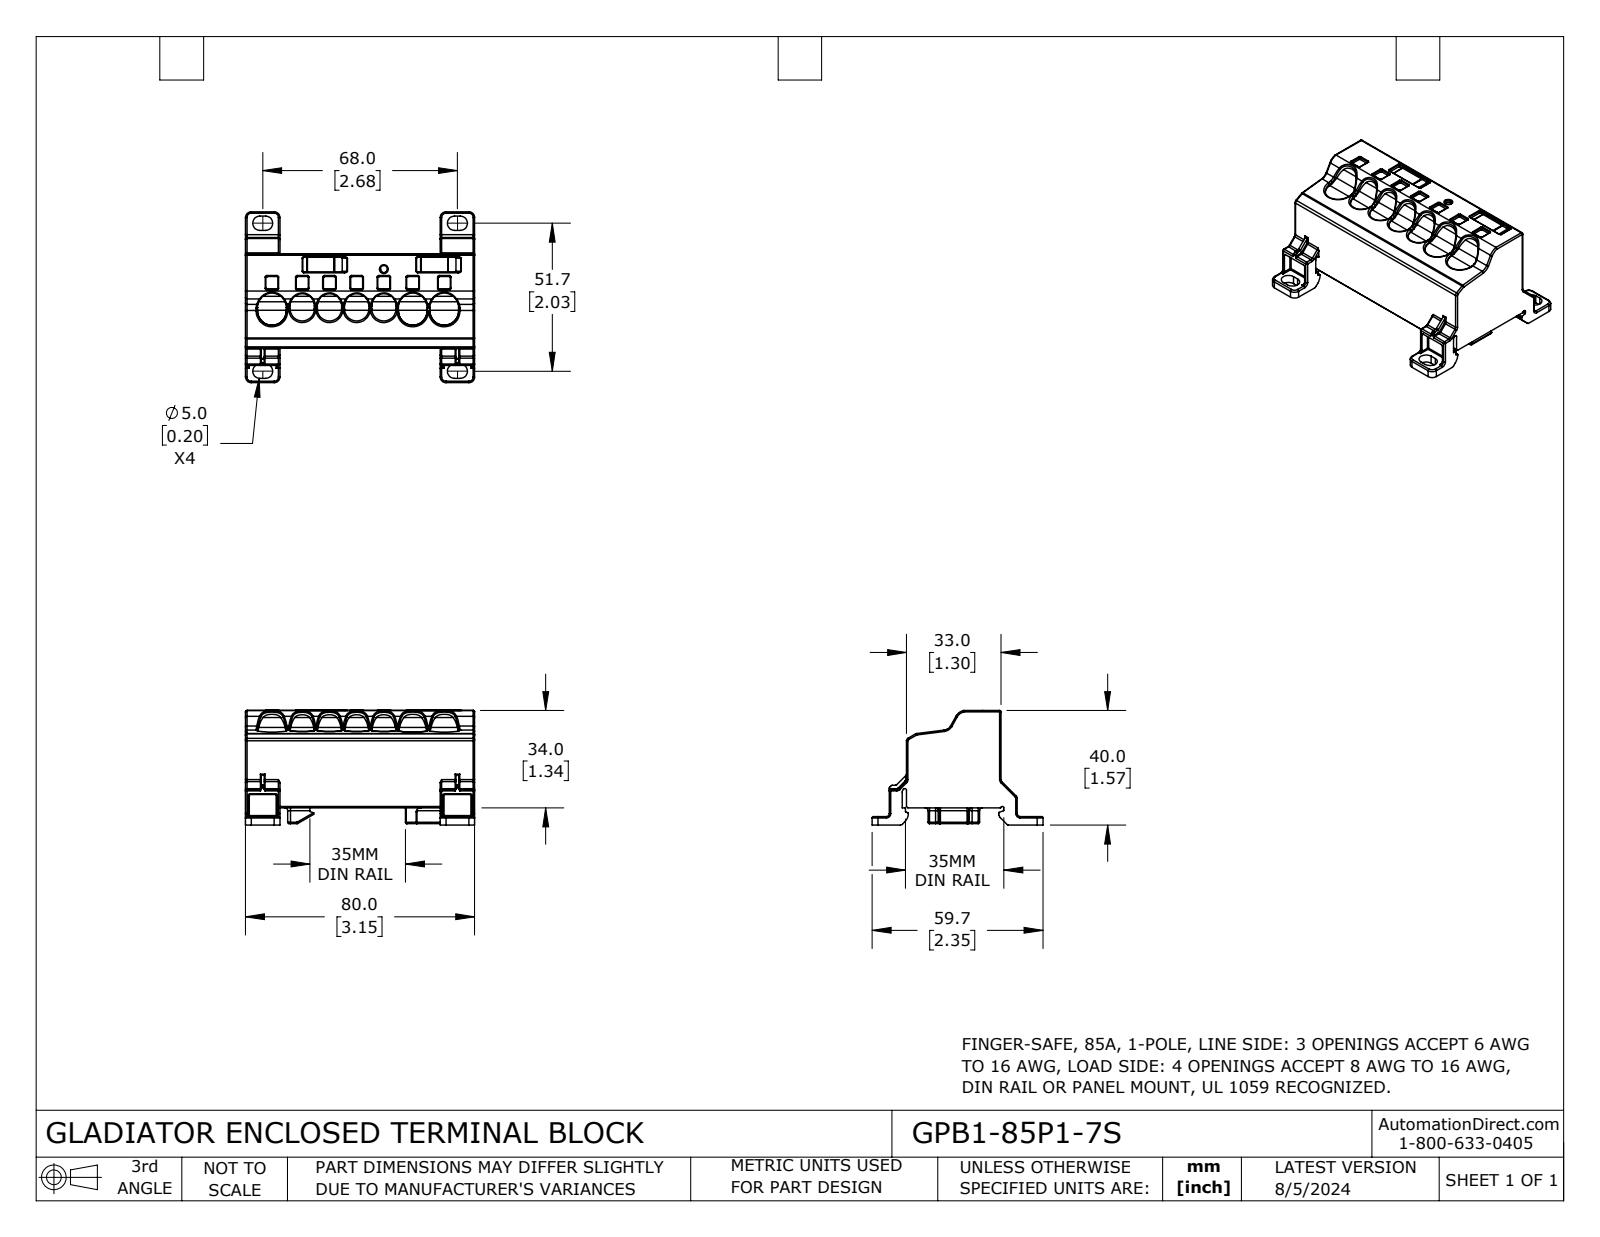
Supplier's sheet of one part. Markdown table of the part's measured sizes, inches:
| quantity | value |
| --- | --- |
| part name | GPB1-85P1-7S |
| STEP written by | SolidWorks 2023 (CONFIG_CONTROL_DESIGN) |
| units | inches |
| bodies | 1 solid, 752 faces (218 planar, 338 cylindrical, 196 other) |
| overall size | 3.15 × 2.349 × 1.575 |
| volume | 5.148 in³ |
| surface area | 25.63 in² |
| round holes (diameter × count) | 0.098 × 1 |
| round bosses / shafts (diameter × count) | 0.197 × 1 |
| partial cylindrical surfaces (radius × count) | 0.02 × 82, 0.012 × 59, 0.01 × 20, 0.039 × 20, 0.008 × 12, 0.079 × 9, 0.098 × 8, 0.167 × 8 |
| main face-to-face distances | 1.299, 3.15, 1.339, 0.118, 0.039, 0.236, 1.575, 0.472, 2.677, 1.417 |
